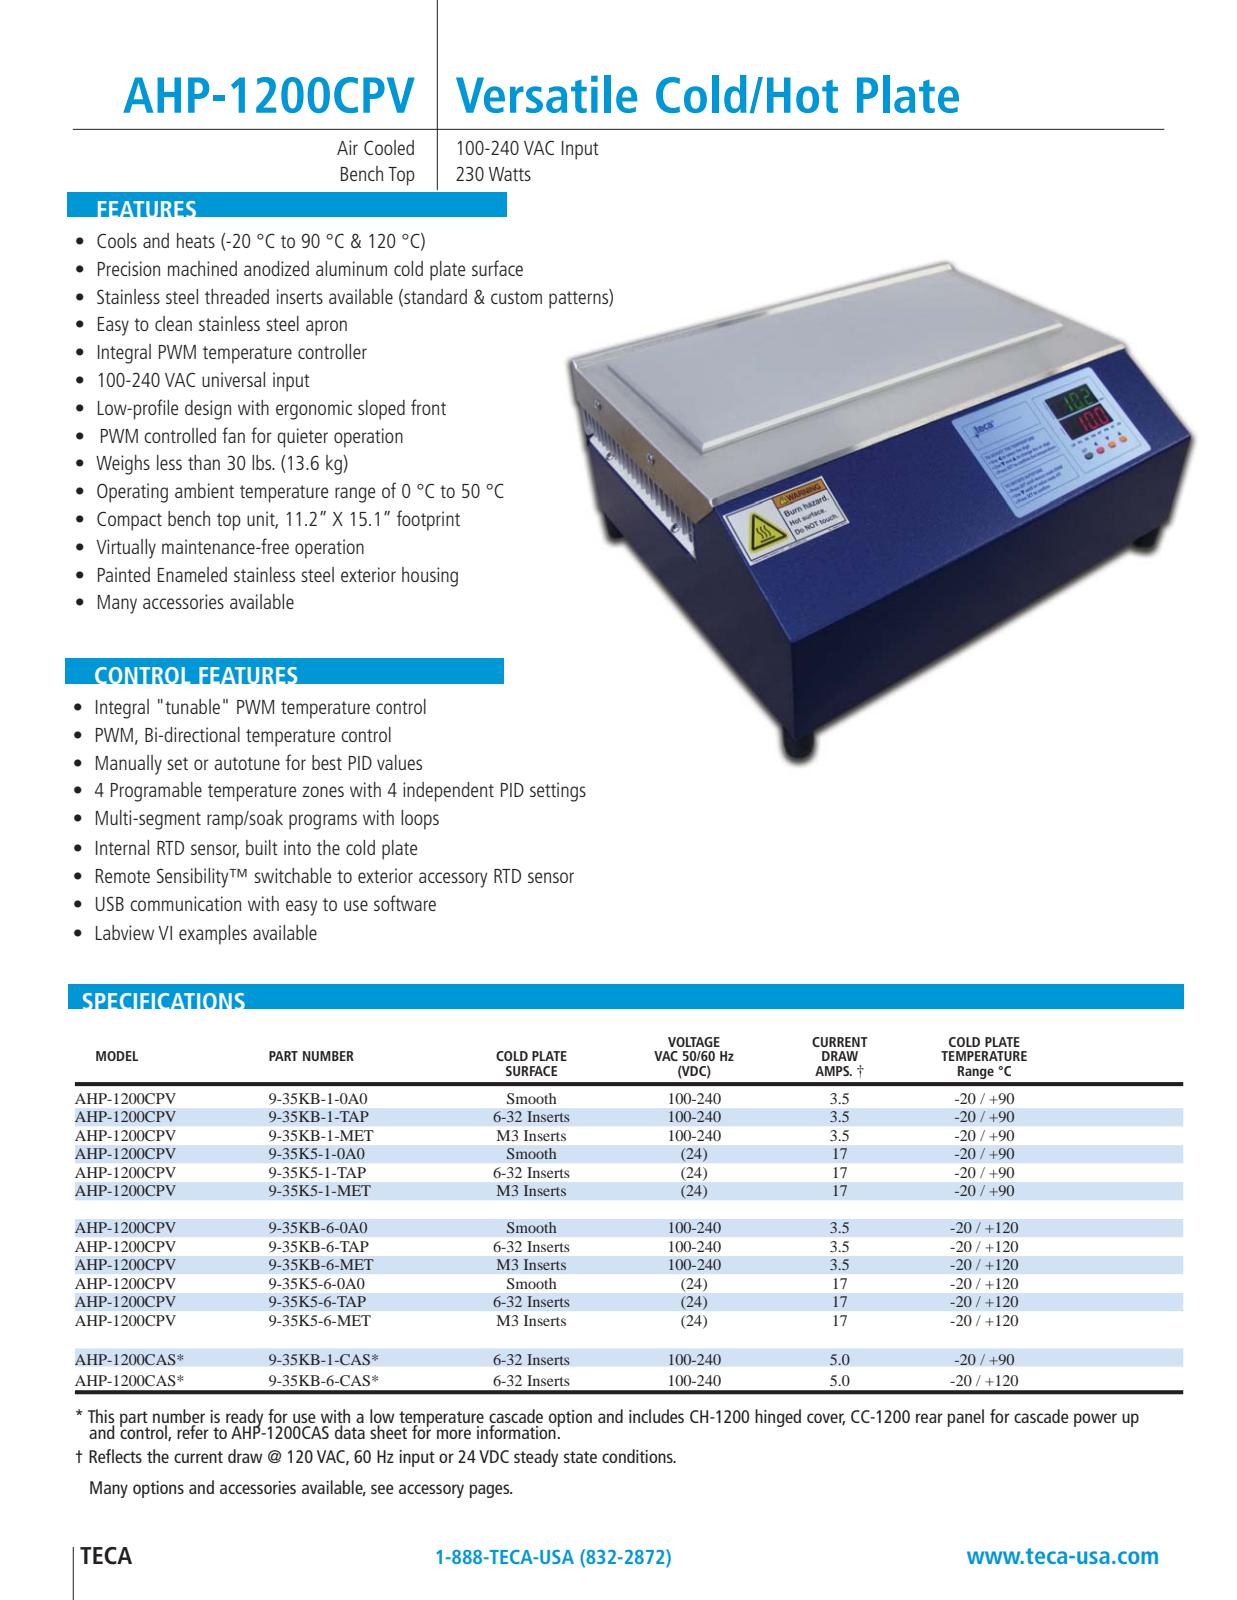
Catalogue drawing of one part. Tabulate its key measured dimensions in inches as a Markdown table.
| quantity | value |
| --- | --- |
| part name | AHP-1200CPV 2nd gen |
| STEP written by | SolidWorks 2015 (CONFIG_CONTROL_DESIGN) |
| units | inches |
| bodies | 0 solids, 2785 faces (1463 planar, 1144 cylindrical, 178 other) |
| overall size | 15.348 × 12.244 × 6.509 |
| round holes (diameter × count) | 0.437 × 4, 0.111 × 2, 2.726 × 1 |
| round bosses / shafts (diameter × count) | 0.238 × 21, 0.75 × 4, 0.321 × 4, 0.27 × 4, 0.22 × 2, 0.219 × 2, 0.118 × 2, 3.004 × 1 |
| partial cylindrical surfaces (radius × count) | 0.09 × 578, 0.012 × 22, 0.02 × 16, 0.03 × 13, 0.039 × 10, 0.024 × 9, 0.08 × 8, 0.25 × 7 |
| main face-to-face distances | 0.048, 0.624, 0.05, 11.758, 0.312, 0.372, 4.041, 0.096, 1.42, 5.461 |
| hole center spacings | 10.93, 14.34, 18.031, 2.7, 7.765, 8.2, 10.153, 10.49 |
